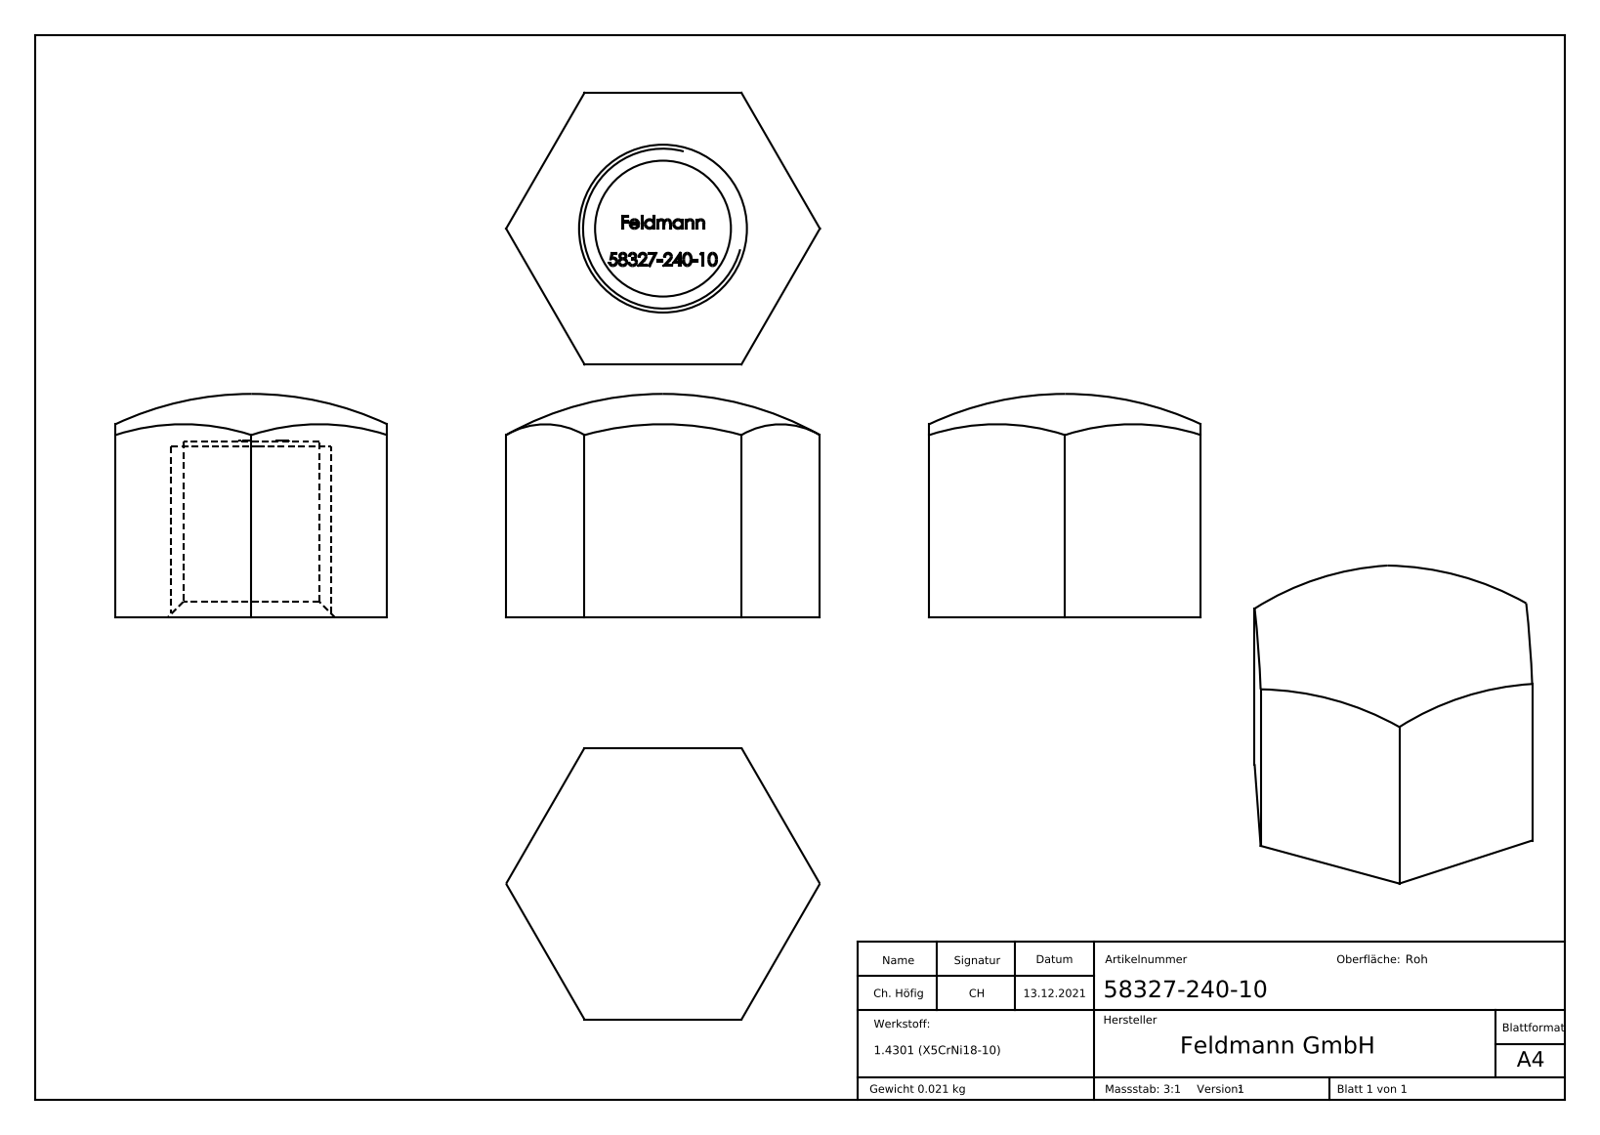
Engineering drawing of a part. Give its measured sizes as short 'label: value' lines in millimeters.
name: 58327-240-10
written by: SolidWorks 2018 (CONFIG_CONTROL_DESIGN)
unit: mm
bodies: 1 solid, 264 faces (144 planar, 1 cylindrical, 119 other)
size: 19.63 × 17 × 14
volume: 2 605 mm³; area: 1 500 mm²
holes: 1× ⌀8.5
face distances: 17, 11, 11.1, 2.45, 0.99, 1.06, 1.78, 0.39, 0.83, 0.79
